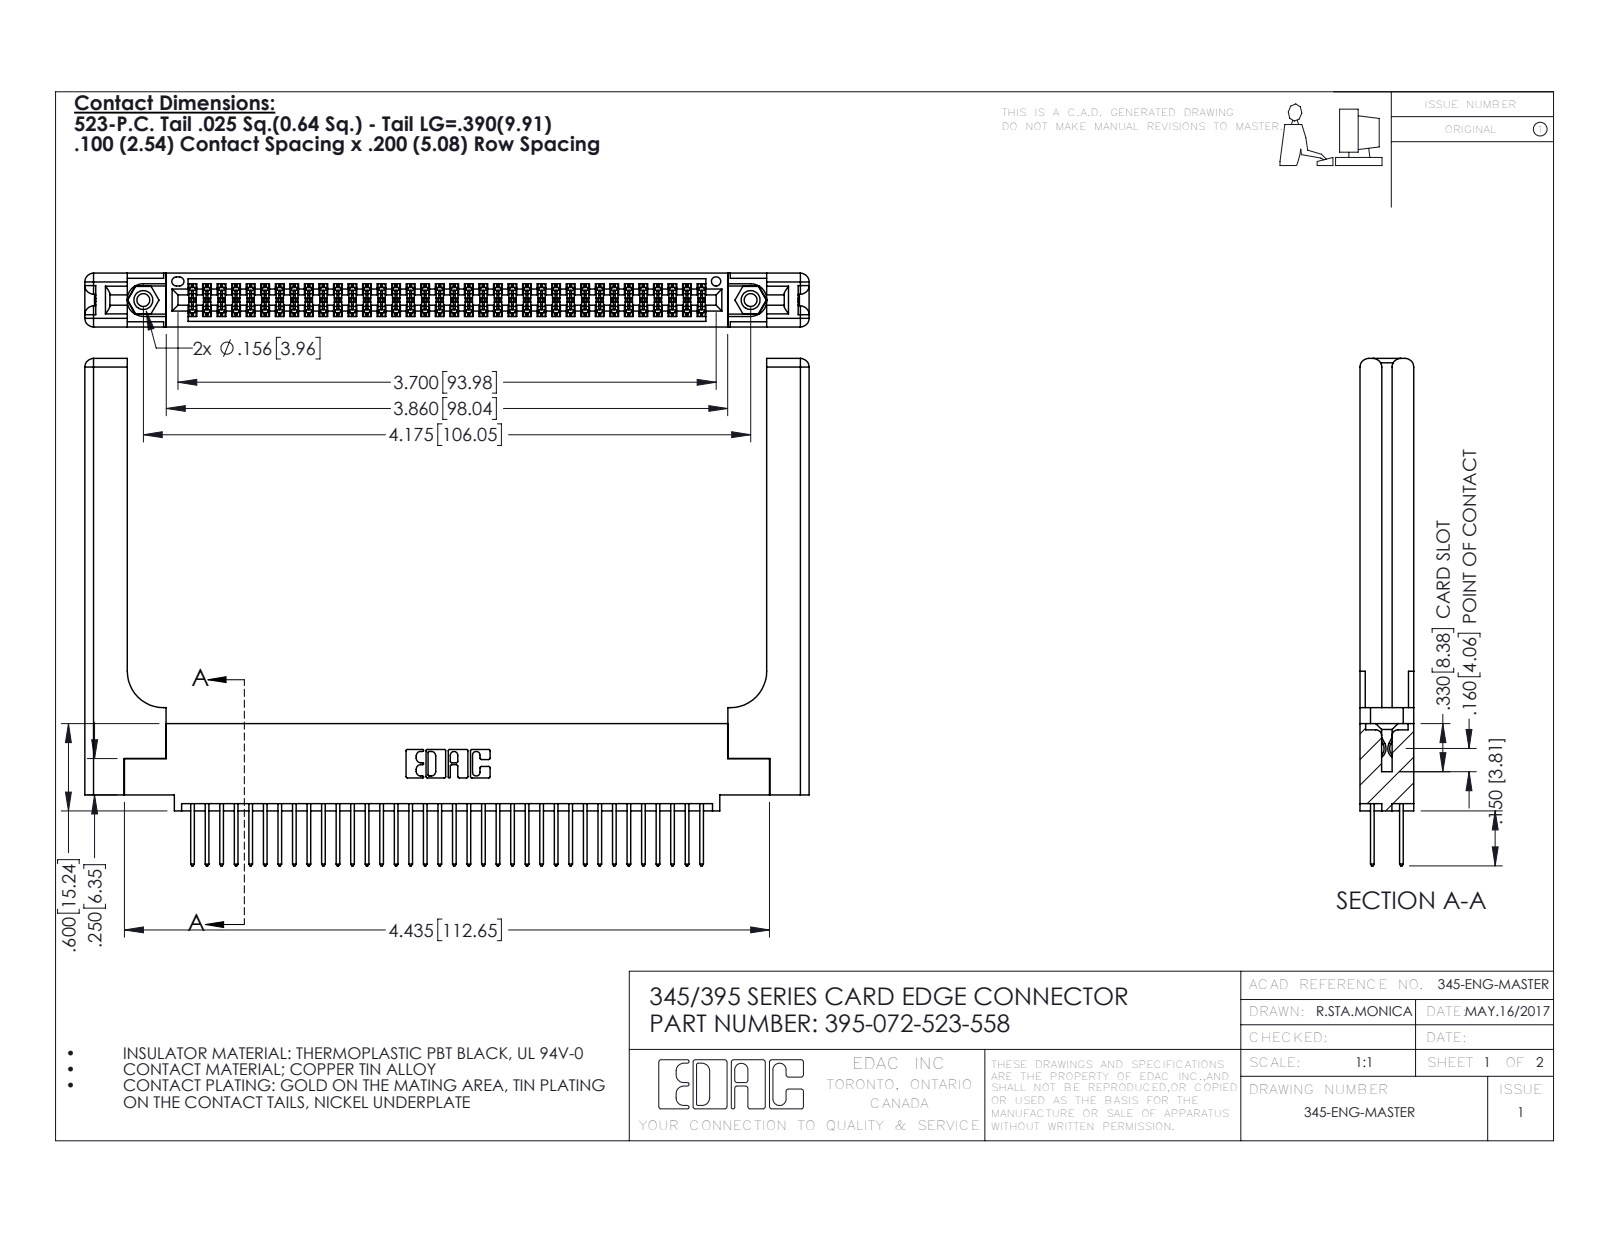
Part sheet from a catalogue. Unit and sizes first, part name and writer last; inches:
Units: inches
Overall size (bounding box): 4.979 × 3.487 × 0.37
Round holes (diameter × count): ⌀0.089 ×2, ⌀0.125 ×2, ⌀0.156 ×2, ⌀0.064 ×1
Round bosses / shafts (diameter × count): ⌀0.155 ×2
Partial cylindrical surfaces — rounded edges, fillets, slot ends (radius × count): R0.006 ×108, R0.01 ×72, R0.01 ×22, R0.06 ×16, R0.007 ×6, R0.031 ×6, R0.026 ×3, R0.014 ×2
Main face-to-face distances: 0.072, 0.298, 0.37, 0.2, 0.098, 0.272, 0.025, 0.225, 0.148, 0.15
Hole centre spacings: 0.27, 3.939, 4.175
Volume: 1.268 in³ · Surface area: 37.02 in²
Bodies: 77 solids, 3986 faces (2608 planar, 1318 cylindrical, 60 other)
Part name (STEP PRODUCT): 345 Part_0.110 Offset - 0.156 Dia-TH; 345-292-001_345-293-123; 345-250-001_345-250-001-102; 395-072-523-558 (+1 more)
STEP written by: SolidWorks 2016 (CONFIG_CONTROL_DESIGN)
